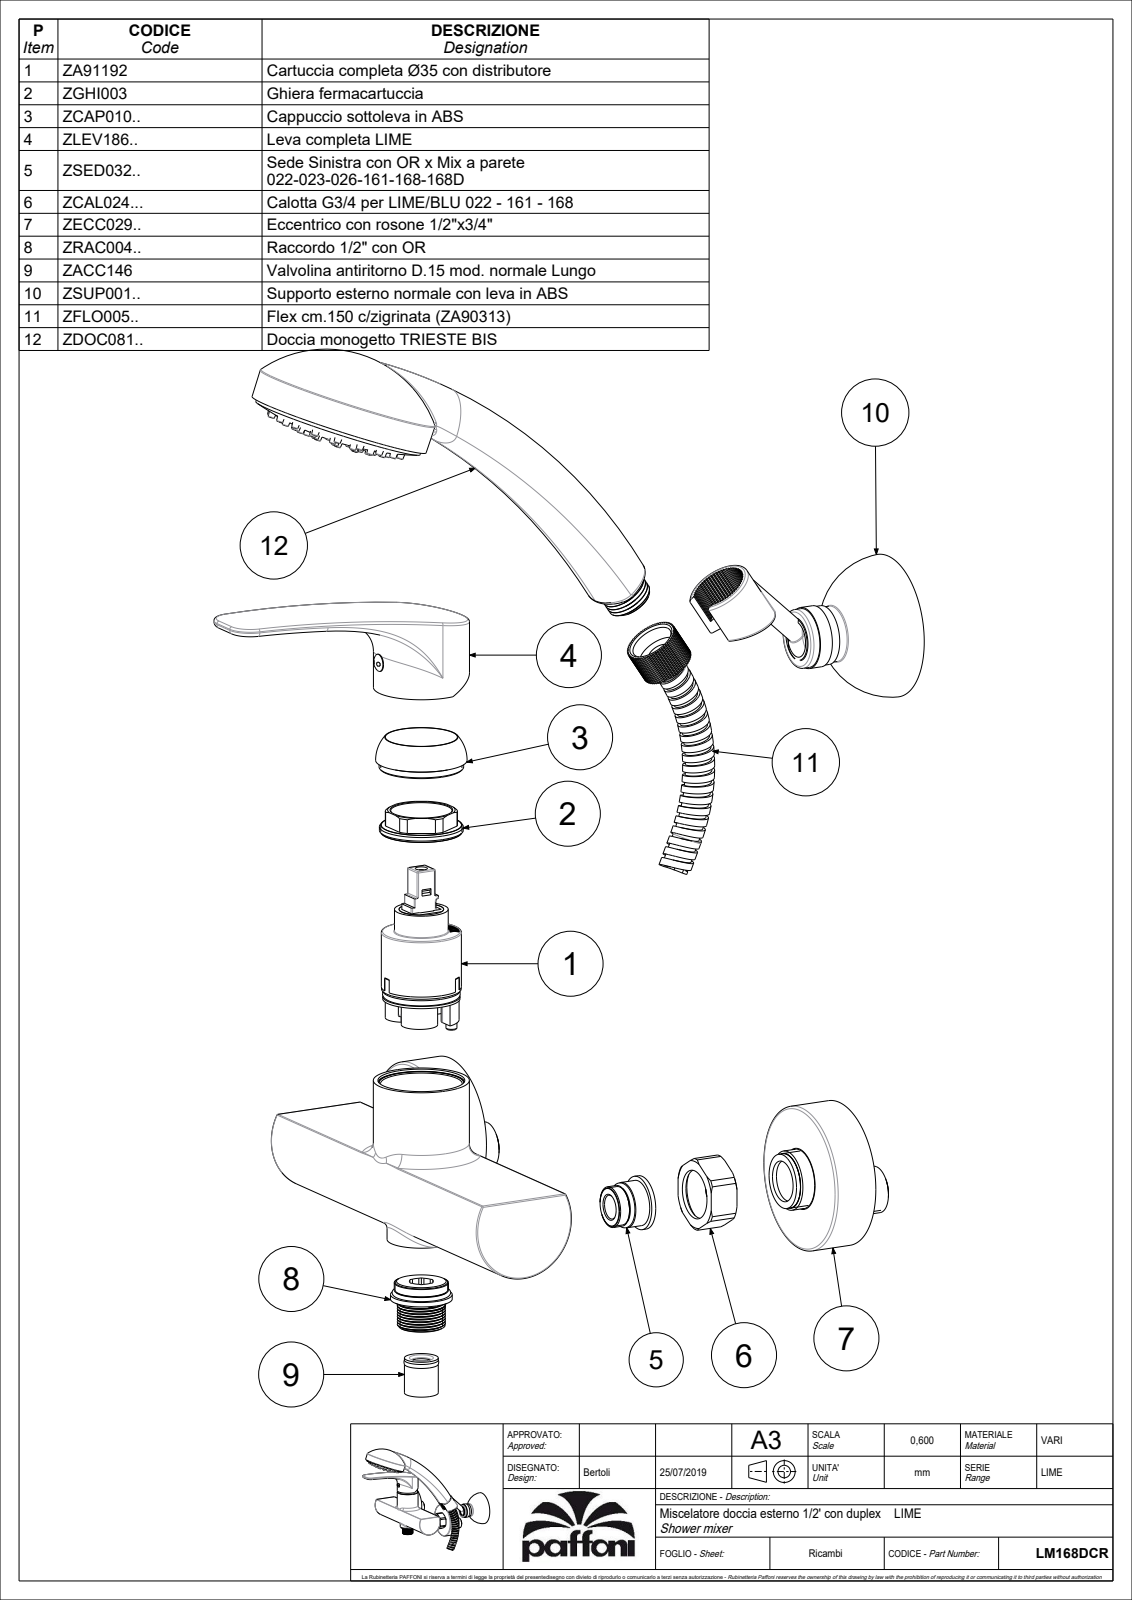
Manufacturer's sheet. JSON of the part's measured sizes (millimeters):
{"part_name": "4111369CRY; 4072081_ROTAZIONE_1; 4072081_ROTAZIONE_2; 4072081_ROTAZIONE_ASM (+8 more)", "step_written_by": "CREO PARAMETRIC BY PTC INC, 2020044 (CONFIG_CONTROL_DESIGN)", "units": "millimeters", "bodies": {"solids": 37, "faces": 2901, "planar": 964, "cylindrical": 743, "other": 1194}, "overall_size": [346.98, 264.67, 244.82], "volume_mm3": 363950, "surface_area_mm2": 277111, "round_holes": [[12, 5], [19, 5], [5, 3], [9, 3], [18, 3], [25, 3], [7, 2], [8, 2], [9.63, 2], [15, 2], [16.3, 2], [16.7, 2]], "round_bosses_or_shafts": [[27, 4], [63.5, 2], [42, 2], [32.2, 2], [29.8, 2], [26.4, 2], [24, 2], [23.8, 2]], "partial_cylinders_radius": [[0.5, 78], [0.3, 26], [1, 18], [0.75, 16], [3, 16], [5, 3], [5.25, 3], [7.25, 3]], "face_to_face_distances": [2.5, 2, 0.6, 67.5, 110, 65, 27, 177.5, 2.8, 112.5], "hole_center_spacings": [0.71, 8.51, 8.6, 9.85, 10.49, 13.04, 13.21, 13.45]}
